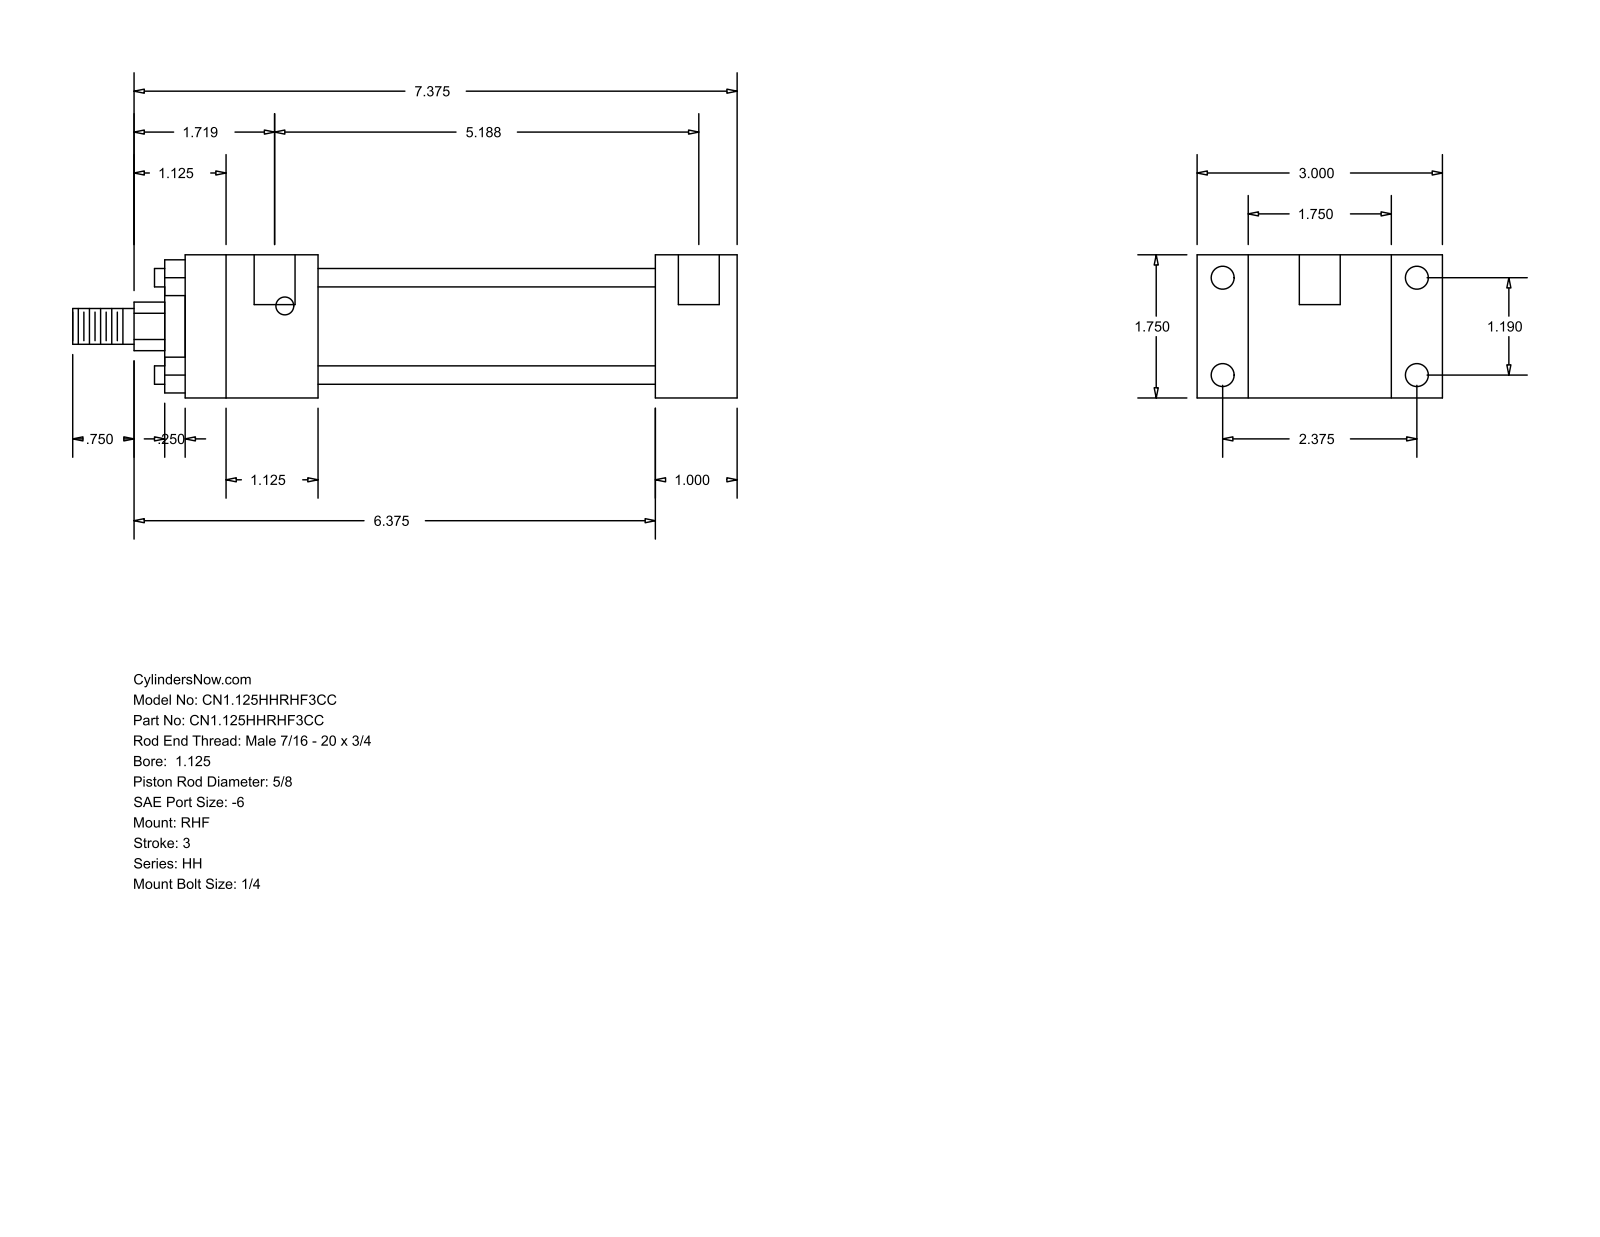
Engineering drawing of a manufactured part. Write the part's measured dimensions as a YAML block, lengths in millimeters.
part_name: "HH_RHF__0112_0.625"
step_written_by: "GSSL Pune (CONFIG_CONTROL_DESIGN)"
units: millimeters
bodies: {solids: 0, faces: 88, planar: 60, cylindrical: 28, other: 0}
overall_size: [206.38, 76.2, 44.45]
round_holes:
  - {diameter: 5.56, count: 4}
  - {diameter: 7.14, count: 4}
  - {diameter: 12.7, count: 2}
round_bosses_or_shafts:
  - {diameter: 5.71, count: 4}
  - {diameter: 34.92, count: 1}
  - {diameter: 28.57, count: 1}
  - {diameter: 15.88, count: 1}
  - {diameter: 11.11, count: 1}
partial_cylinders:
  - {radius: 7.54, count: 1}
face_to_face_distances: [44.46, 15.87, 60.33, 25.39, 76.2, 104.78, 130.17, 41.27, 146.05, 171.44]
hole_center_spacings: [30.22, 60.32, 67.47, 128.59, 3.17, 131.76]
